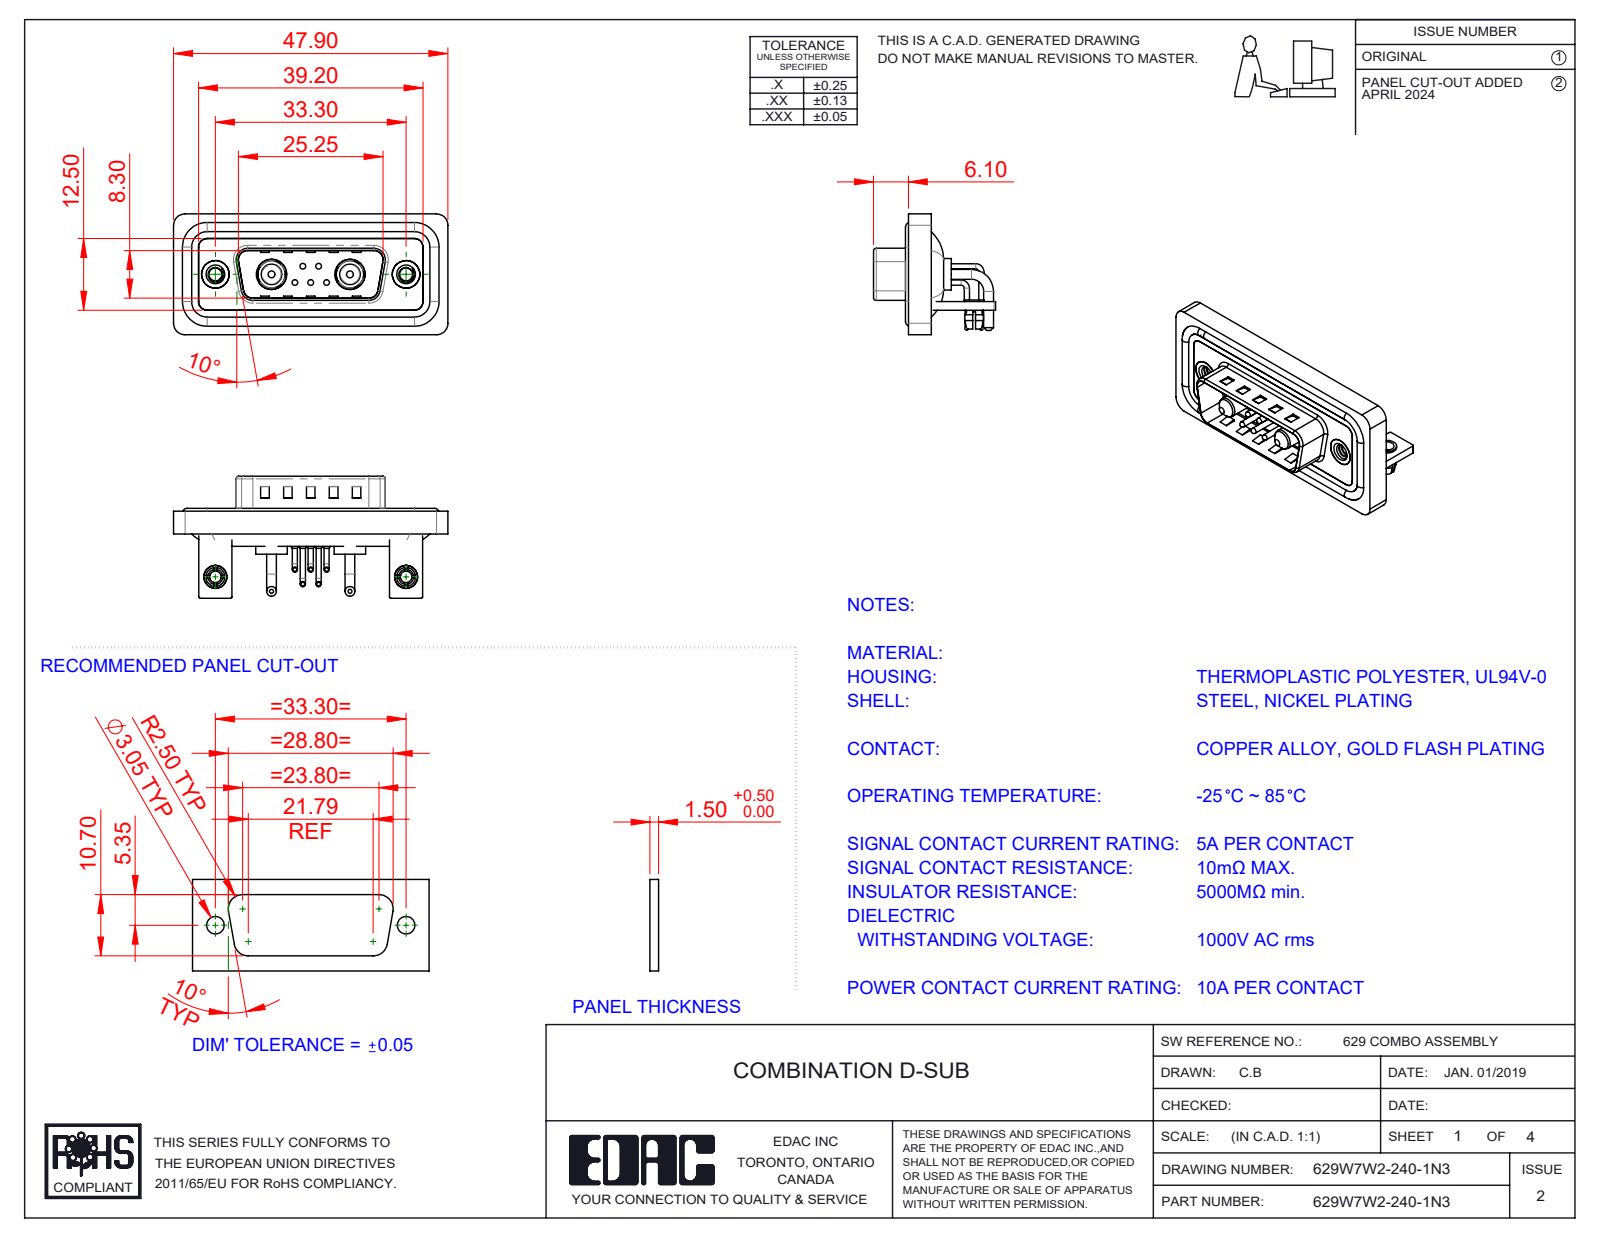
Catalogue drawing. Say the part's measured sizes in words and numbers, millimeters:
The part is named "629W7W2-140-1N3; 629Combo Shell Rear_15 Contacts; Power Pin_10A RA; 629Combo Contact Row 2 (+7 more)". Its 3-D file was written by "SolidWorks 2023 (CONFIG_CONTROL_DESIGN)". It is 20 solids with 1215 faces: 585 planar, 456 cylindrical and 174 other. Overall it measures 47.9 by 21.3 by 21.1 millimeters. Its volume is 5 878 cubic millimeters and its surface area 9 836 square millimeters. Round holes: 7 of diameter 2, 5 of diameter 0.75, 5 of diameter 1.6, 2 of diameter 2.26, 2 of diameter 2.5, 2 of diameter 3.2, 2 of diameter 4, 2 of diameter 4.8, 2 of diameter 4.85, 2 of diameter 5, 2 of diameter 5.3. Round bosses or shafts: 10 of diameter 0.9, 5 of diameter 1.5, 5 of diameter 1, 5 of diameter 0.65, 4 of diameter 1.7, 4 of diameter 1.6, 2 of diameter 5.5, 2 of diameter 5.2. Partial cylindrical surfaces (rounded edges, fillets, slot ends): 21 of radius 2, 18 of radius 1.5, 16 of radius 0.25, 9 of radius 0.5, 8 of radius 1.6, 5 of radius 1.01, 4 of radius 0.6, 4 of radius 0.65. The main face-to-face distances are 0.4, 1.5, 0.8, 2.9, 2.1, 1.1, 1.6, 1.2, 3.7, 4.5. The hole center spacings are 3.16, 2.77, 9.8, 23.5, 33.3, 4.31, 4.33, 5.03.
